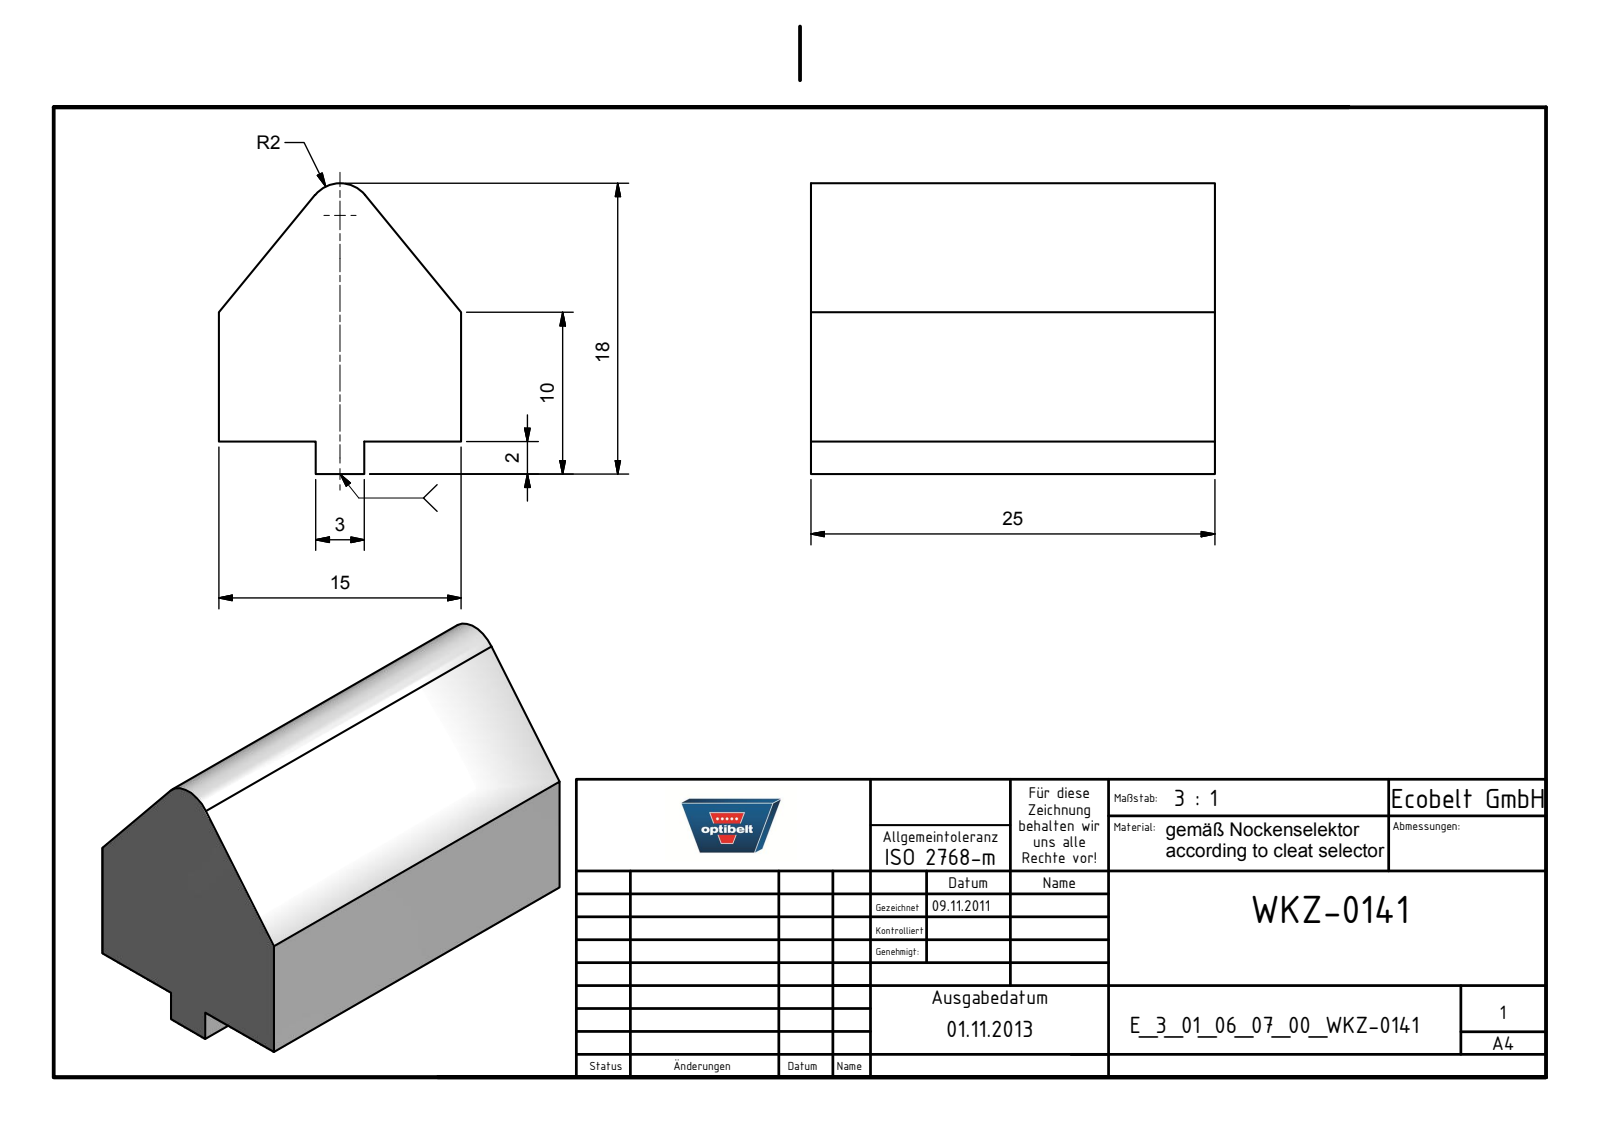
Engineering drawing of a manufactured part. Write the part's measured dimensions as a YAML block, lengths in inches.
part_name: "E_3_01_06_07_00_WKZ-0141"
step_written_by: "Autodesk Inventor 2025 (AUTOMOTIVE_DESIGN)"
units: inches
bodies: {solids: 1, faces: 12, planar: 11, cylindrical: 1, other: 0}
overall_size: [0.984, 0.709, 0.591]
volume: 0.295
surface_area: 2.821
partial_cylinders:
  - {radius: 0.079, count: 1}
face_to_face_distances: [0.591, 0.984, 0.236, 0.354, 0.079, 0.118]
